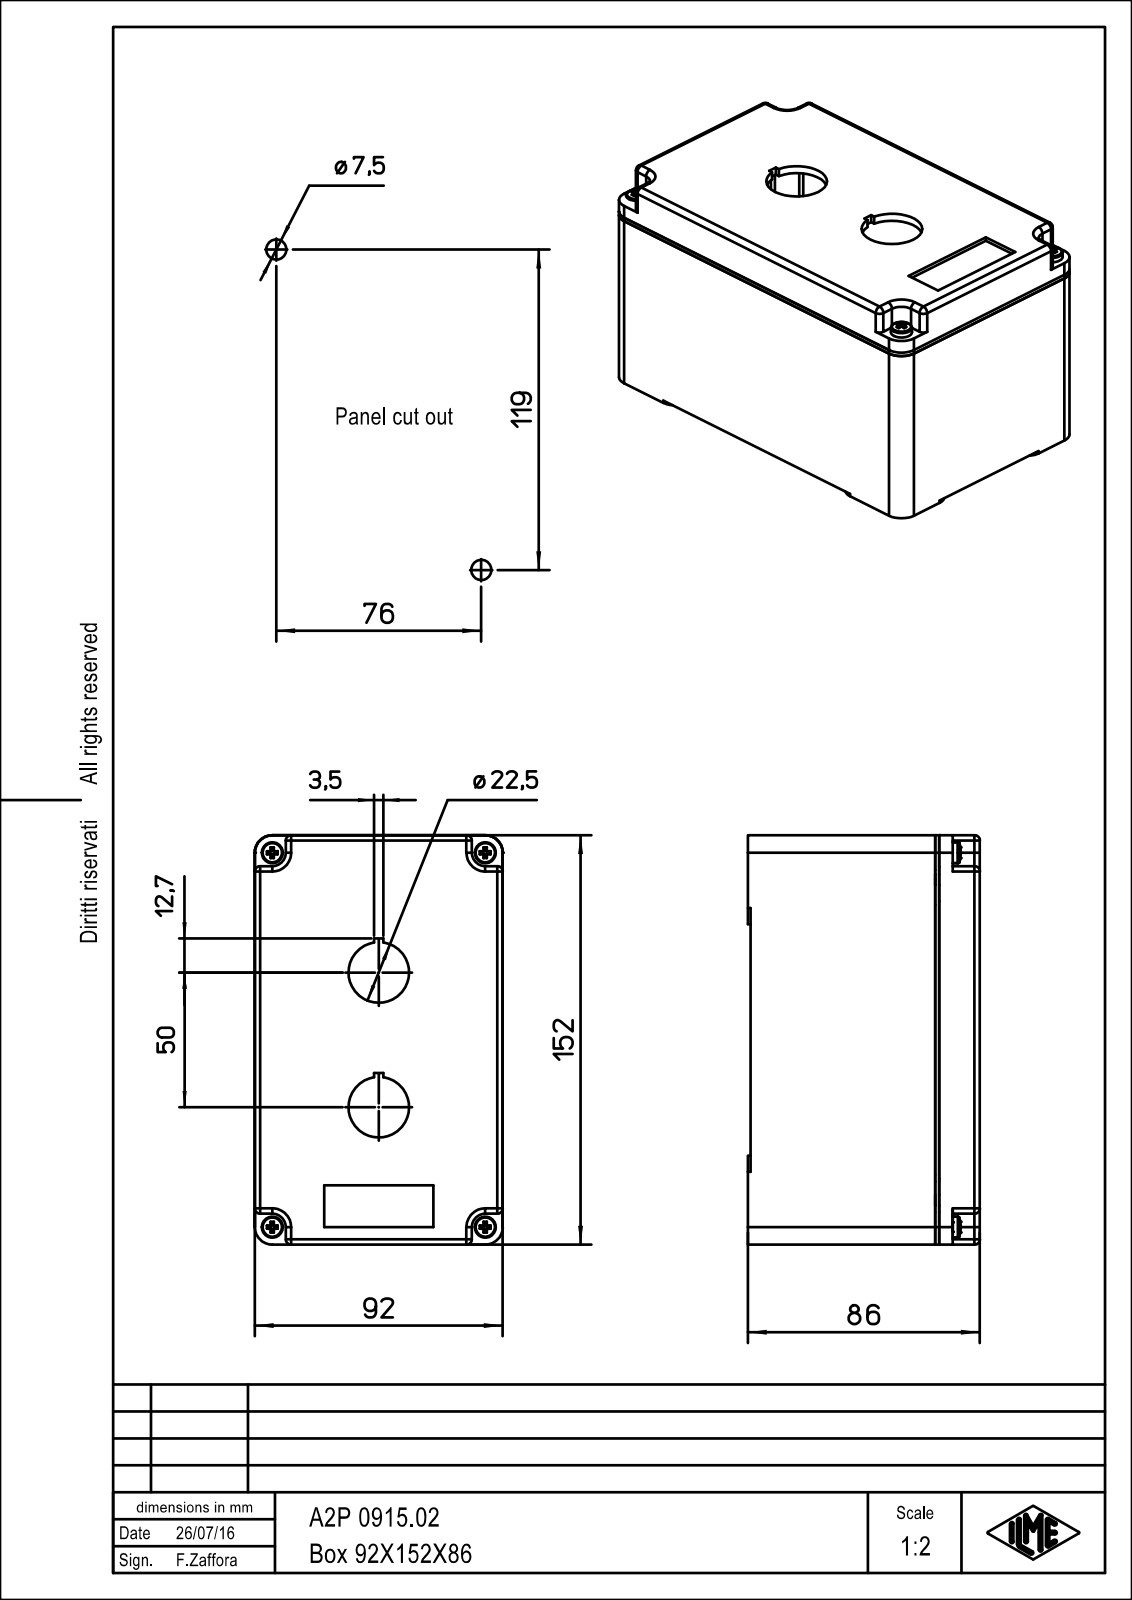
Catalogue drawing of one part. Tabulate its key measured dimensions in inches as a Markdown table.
| quantity | value |
| --- | --- |
| part name | BOX; COVER; A2P_0915.02 |
| STEP written by | PTC Creo Elements/Direct Modeling 19.0B 21-Mar-2015 (C) Parametric Technology GmbH (AUTOMOTIVE_DESIGN) |
| units | inches |
| bodies | 2 solids, 1004 faces (793 planar, 171 cylindrical, 40 other) |
| overall size | 5.984 × 3.623 × 3.386 |
| volume | 17.94 in³ |
| surface area | 226.7 in² |
| round holes (diameter × count) | 0.13 × 6, 0.177 × 4, 0.228 × 2, 0.295 × 2, 0.886 × 2, 0.417 × 1, 0.418 × 1 |
| round bosses / shafts (diameter × count) | 0.307 × 4, 0.157 × 4, 0.244 × 2, 0.236 × 2, 0.276 × 1 |
| partial cylindrical surfaces (radius × count) | 0.013 × 22, 0.079 × 17, 0.236 × 12, 0.256 × 12, 0.197 × 6, 0.315 × 6, 0.011 × 4, 0.011 × 4 |
| main face-to-face distances | 0.118, 3.228, 0.172, 3.622, 0.172, 3.346, 3.11, 0.531, 2.579, 2.697 |
| hole center spacings | 3.11, 2.343, 3.076, 4.032, 5.472, 6.294, 0.398, 0.459 |
